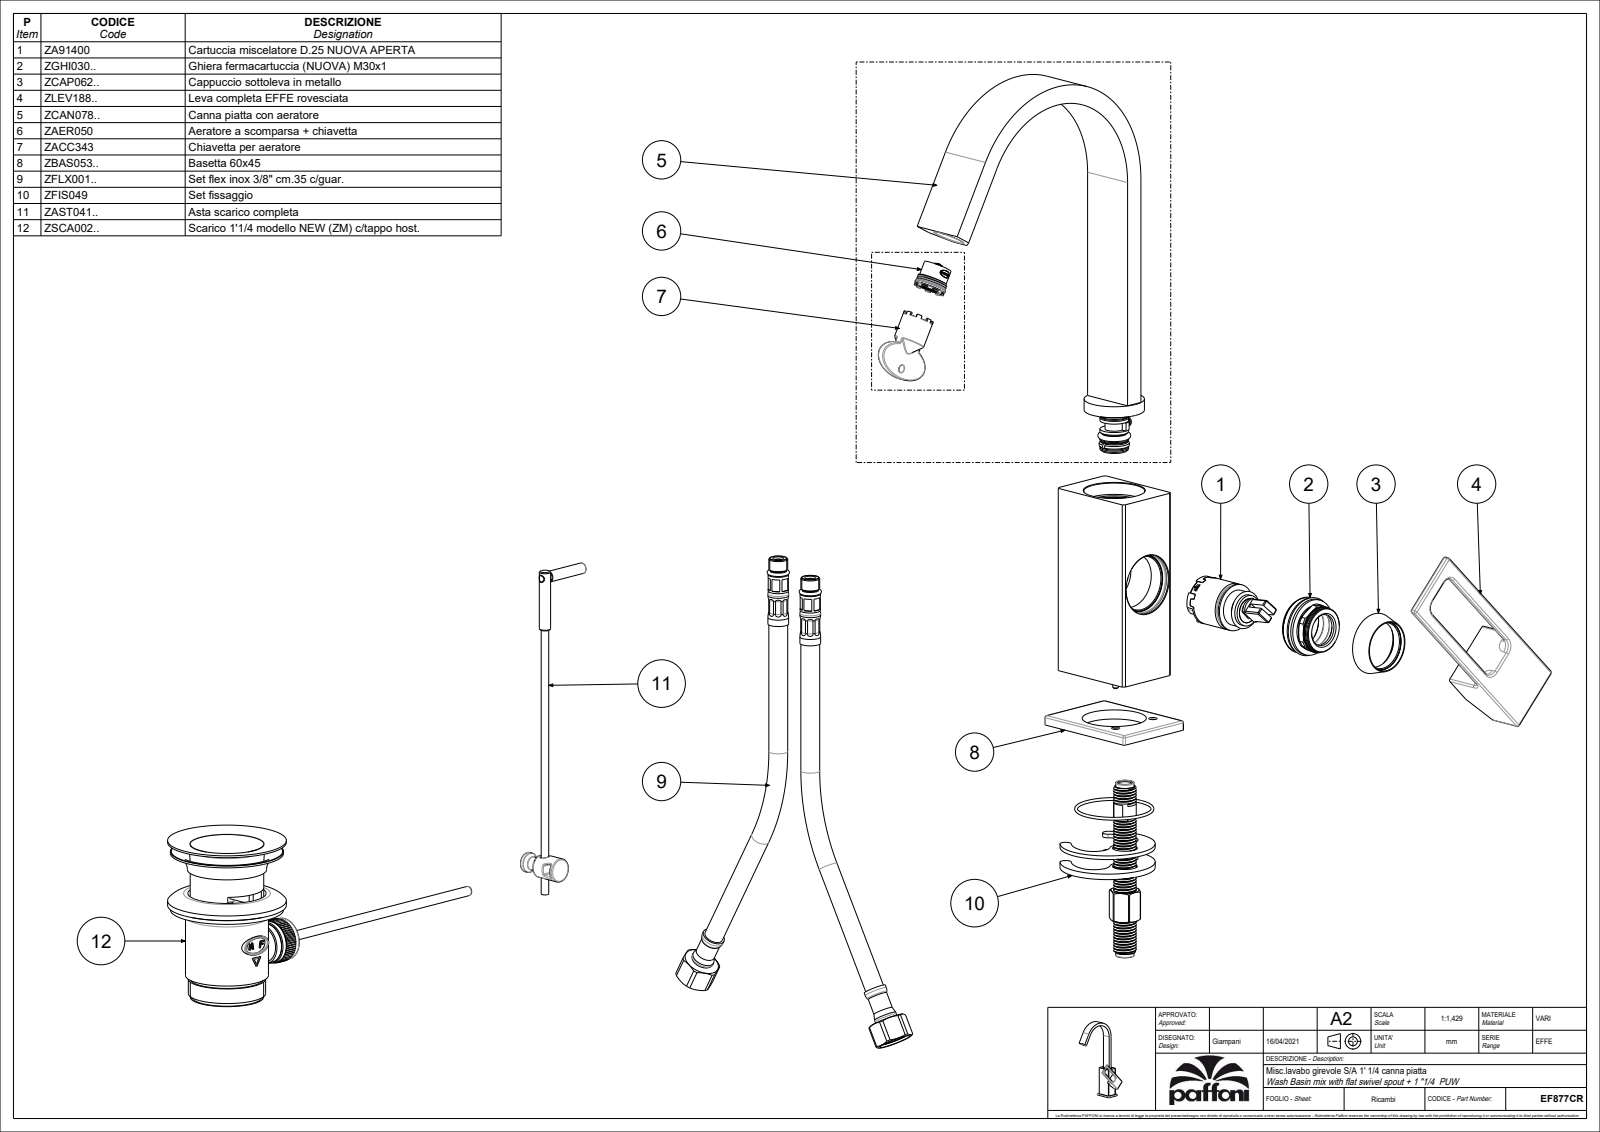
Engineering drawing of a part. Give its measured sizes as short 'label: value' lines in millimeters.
name: EF877CR
written by: CREO PARAMETRIC BY PTC INC, 2020044 (CONFIG_CONTROL_DESIGN)
unit: mm
bodies: 6 solids, 2723 faces (1901 planar, 533 cylindrical, 289 other)
size: 290.2 × 160.93 × 83.28
volume: 221 415 mm³; area: 105 564 mm²
holes: 4× ⌀4.5, 3× ⌀3.3, 3× ⌀5, 3× ⌀6, 3× ⌀7, 2× ⌀3, 2× ⌀3.2, 2× ⌀5.5, 2× ⌀6.5, 1× ⌀4, 1× ⌀7.8, 1× ⌀8
bosses: 3× ⌀0.9, 2× ⌀12, 2× ⌀10.5, 2× ⌀9, 2× ⌀7.6, 1× ⌀38.8, 1× ⌀32, 1× ⌀20
rounds: 51× R0.12, 28× R1, 8× R1.5, 6× R0.6, 5× R5, 2× R3, 1× R7.46, 1× R30
face distances: 1.5, 10, 13, 23, 8.5, 21.5, 36, 14.5, 40, 11.5
hole spacings: 6.72, 8.95, 9.34, 9.43, 10.12, 11.2, 11.31, 15.26
